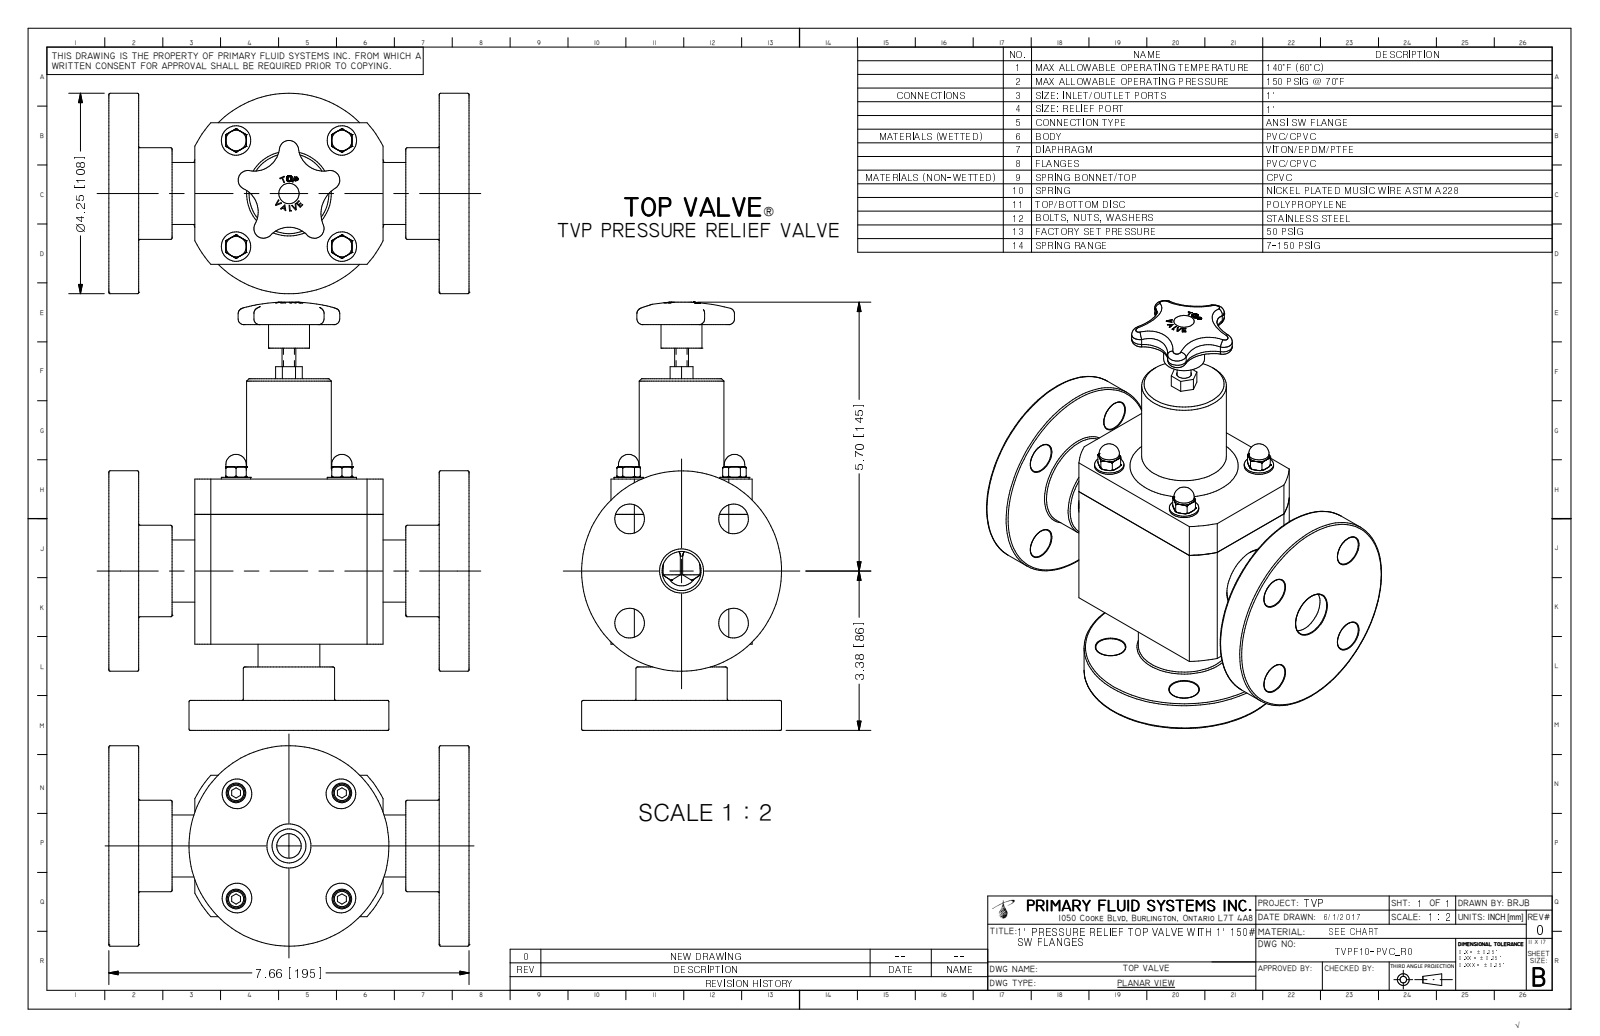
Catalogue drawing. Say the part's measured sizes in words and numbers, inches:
The part is named "TVPF10-PVC_R0". Its 3-D file was written by "Autodesk Inventor 2009 (AUTOMOTIVE_DESIGN)". It is 1 solid with 424 faces: 157 planar, 70 cylindrical and 197 other. Overall it measures 9.08 by 7.659 by 4.25 inches. Its volume is 74.75 cubic inches and its surface area 283.1 square inches. Round holes: 8 of diameter 0.63, 4 of diameter 0.175, 2 of diameter 0.936, 2 of diameter 0.957. Round bosses or shafts: 4 of diameter 0.625, 4 of diameter 0.433, 4 of diameter 0.375, 2 of diameter 4.25, 2 of diameter 1.941, 2 of diameter 1.315, 1 of diameter 1.8, 1 of diameter 0.87. Partial cylindrical surfaces (rounded edges, fillets, slot ends): 5 of radius 0.085, 5 of radius 0.205, 4 of radius 0.536, 4 of radius 0.656, 1 of radius 0.625, 1 of radius 0.745, 1 of radius 2.238. The main face-to-face distances are 0.635, 7.024, 3, 7.659, 1.83, 5.83, 1.194, 5.194, 1.83, 1.195. The hole center spacings are 1.562, 2.209, 2.23, 2.23, 2.25, 3.125, 3.153, 0.029.
